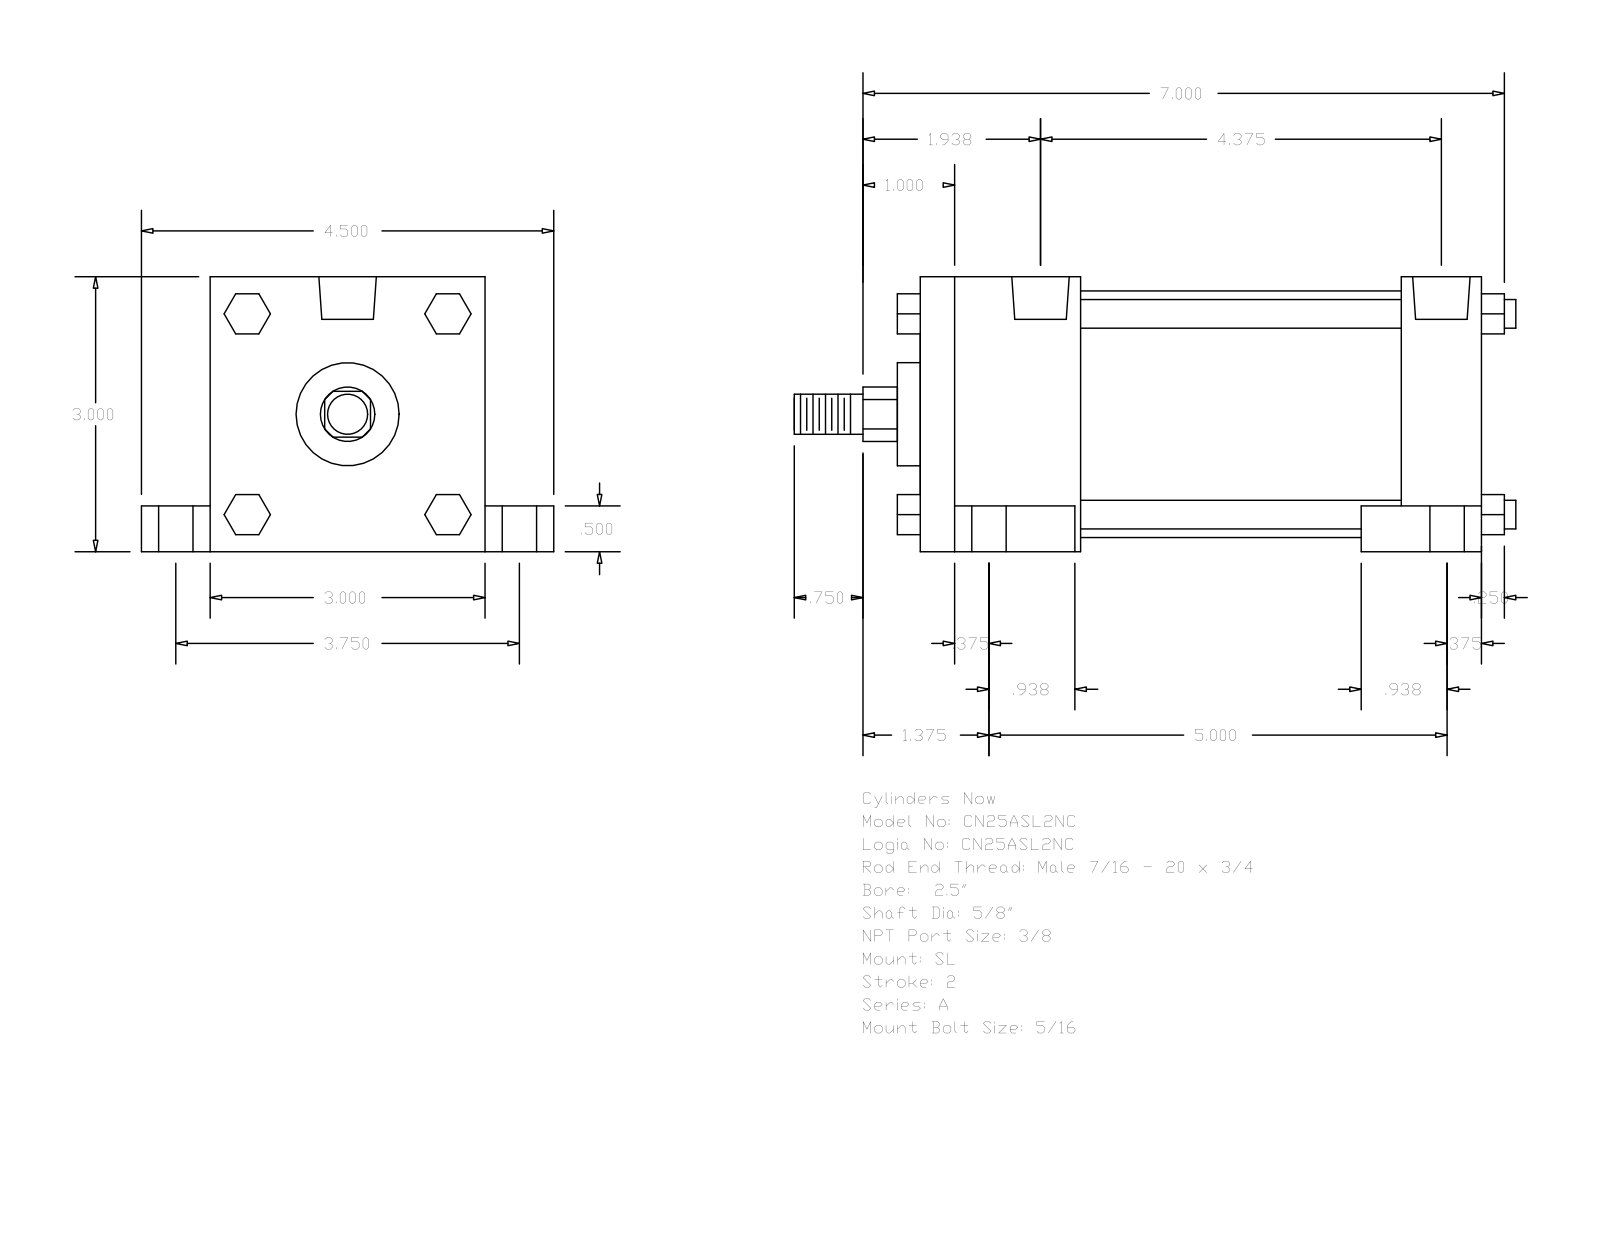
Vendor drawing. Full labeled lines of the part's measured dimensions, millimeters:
Part name (STEP PRODUCT): A_SL__0250_0.625
STEP written by: GSSL Pune (CONFIG_CONTROL_DESIGN)
Units: millimetres
Bodies: 0 solids, 148 faces (112 planar, 36 cylindrical, 0 other)
Overall size (bounding box): 200.03 × 114.3 × 76.2
Round holes (diameter × count): ⌀5.56 ×4, ⌀9.53 ×4, ⌀15.88 ×4, ⌀15.93 ×2
Round bosses / shafts (diameter × count): ⌀7.94 ×4, ⌀68.33 ×1, ⌀28.57 ×1, ⌀15.88 ×1, ⌀11.11 ×1
Partial cylindrical surfaces — rounded edges, fillets, slot ends (radius × count): R7.54 ×1
Main face-to-face distances: 76.2, 155.57, 44.45, 111.12, 133.34, 88.89, 22.23, 63.5, 12.7, 19.05
Hole centre spacings: 2.38, 47.63, 47.65, 49.09, 49.72, 95.24, 113.51, 115.89
